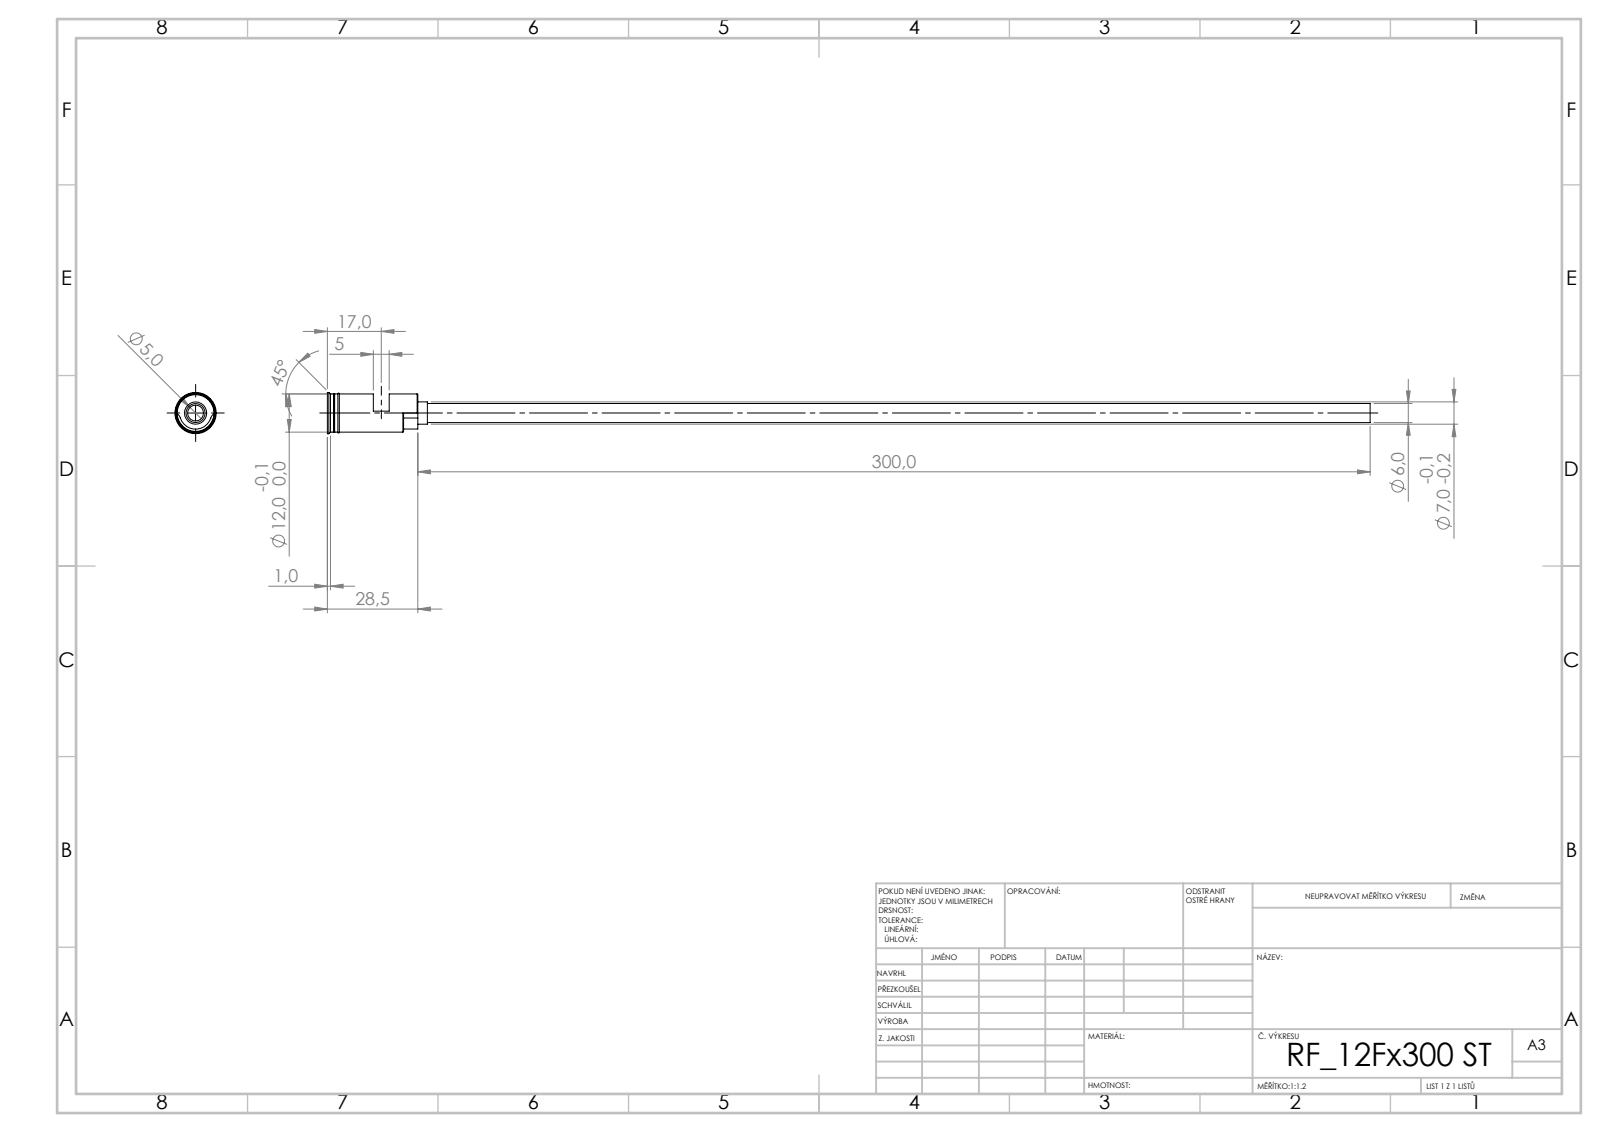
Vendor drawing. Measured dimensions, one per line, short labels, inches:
written by: SolidWorks 2019 (CONFIG_CONTROL_DESIGN)
unit: in
bodies: 1 solid, 55 faces (24 planar, 19 cylindrical, 12 other)
size: 12.933 × 0.512 × 0.512
volume: 0.317 in³; area: 18.58 in²
holes: 1× ⌀0.197
bosses: 1× ⌀0.512, 1× ⌀0.472, 1× ⌀0.465, 1× ⌀0.276, 1× ⌀0.236
rounds: 2× R0.118, 1× R0.199
face distances: 0.571, 0.492, 0.079, 0.551, 1.043, 1.122, 0.354, 0.197, 0.689, 0.768
